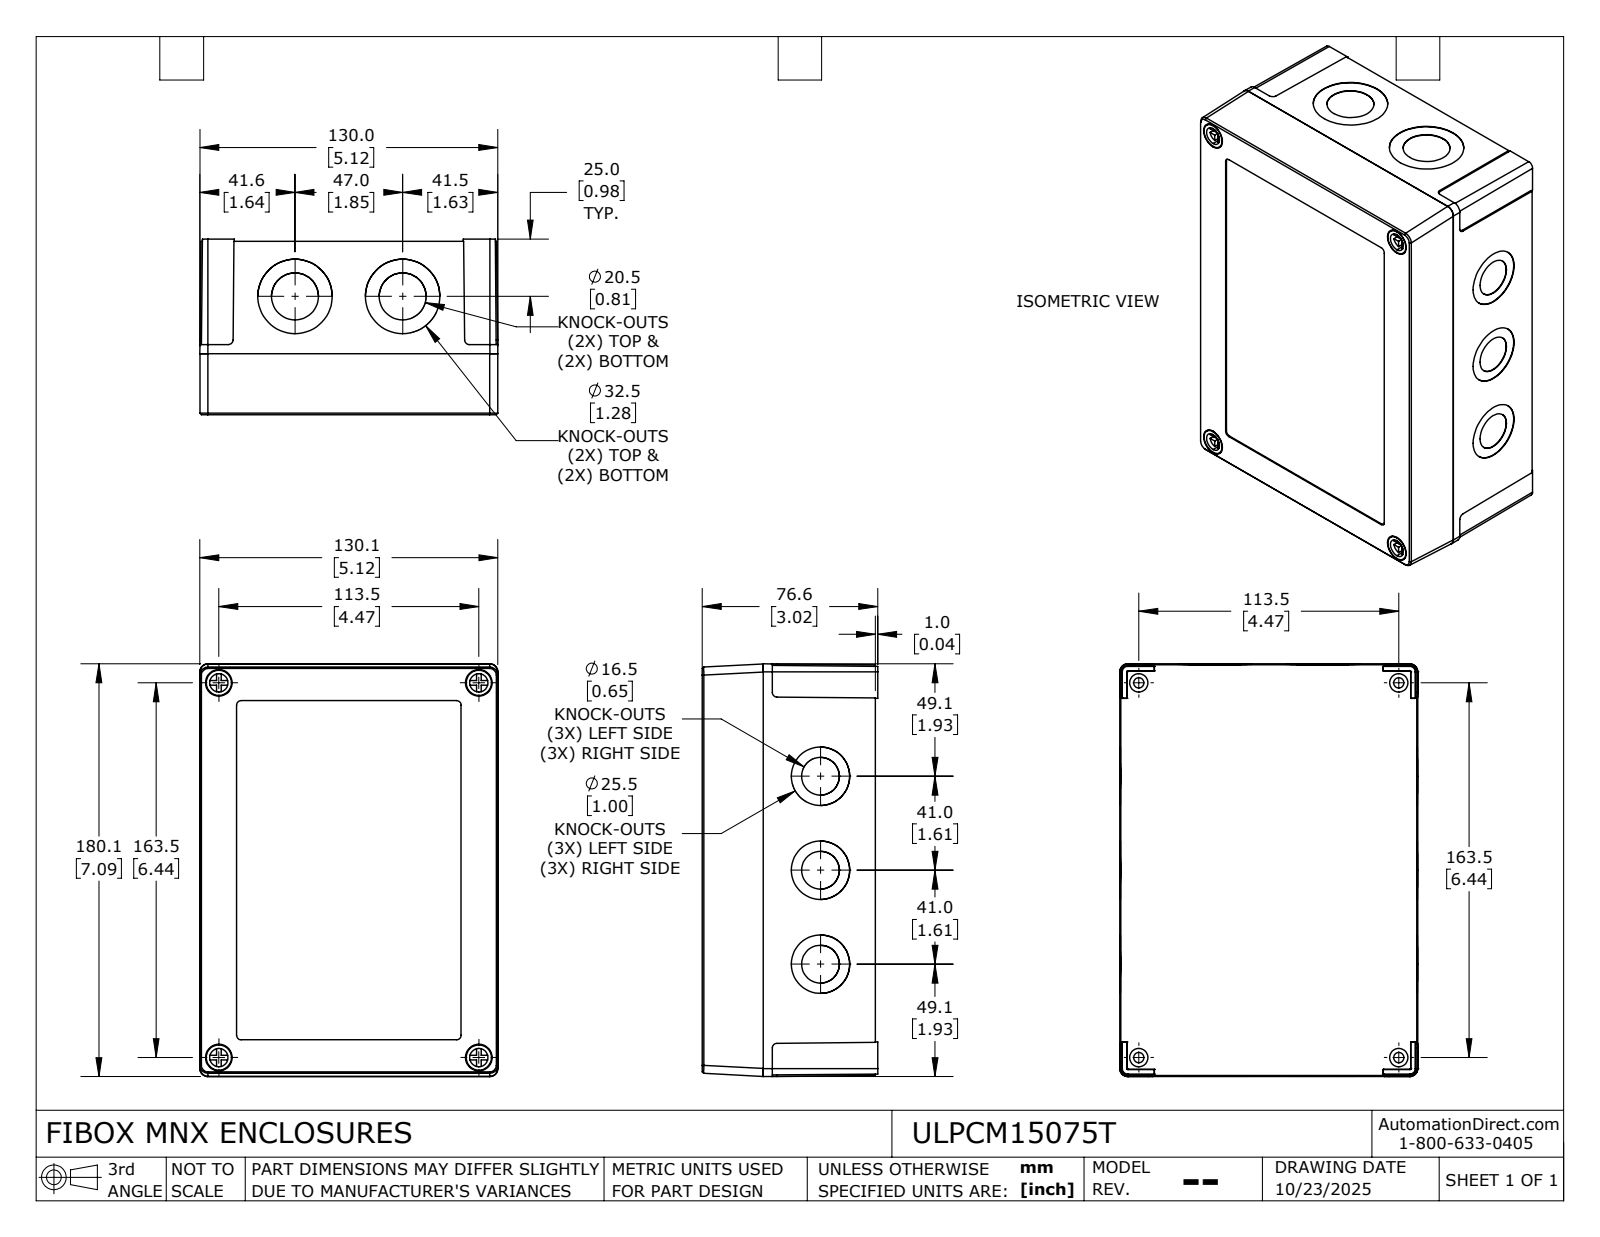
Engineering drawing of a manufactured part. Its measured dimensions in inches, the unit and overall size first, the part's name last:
Units: inches
Overall size (bounding box): 7.091 × 5.122 × 3.016
Round holes (diameter × count): ⌀0.126 ×8, ⌀0.157 ×8, ⌀0.65 ×6, ⌀1.004 ×6, ⌀0.177 ×4, ⌀0.315 ×4, ⌀0.457 ×4, ⌀0.807 ×4, ⌀1.28 ×4
Round bosses / shafts (diameter × count): ⌀0.315 ×8, ⌀0.098 ×8, ⌀0.433 ×4, ⌀0.283 ×4
Partial cylindrical surfaces — rounded edges, fillets, slot ends (radius × count): R0.079 ×8, R0.056 ×6, R0.021 ×4, R0.138 ×4, R0.197 ×4, R0.023 ×2
Main face-to-face distances: 2.878, 0.118, 2.76, 0.165, 0.079, 2.839, 2.957, 2.858, 0.098, 0.02
Hole centre spacings: 1.333, 1.614, 1.939, 1.969, 2.281, 3.252, 3.276, 4.054
Volume: 19.28 in³ · Surface area: 302.8 in²
Bodies: 6 solids, 534 faces (302 planar, 196 cylindrical, 36 other)
Part name (STEP PRODUCT): ULPCM15075T_Default
STEP written by: SolidWorks 2024 (CONFIG_CONTROL_DESIGN)
